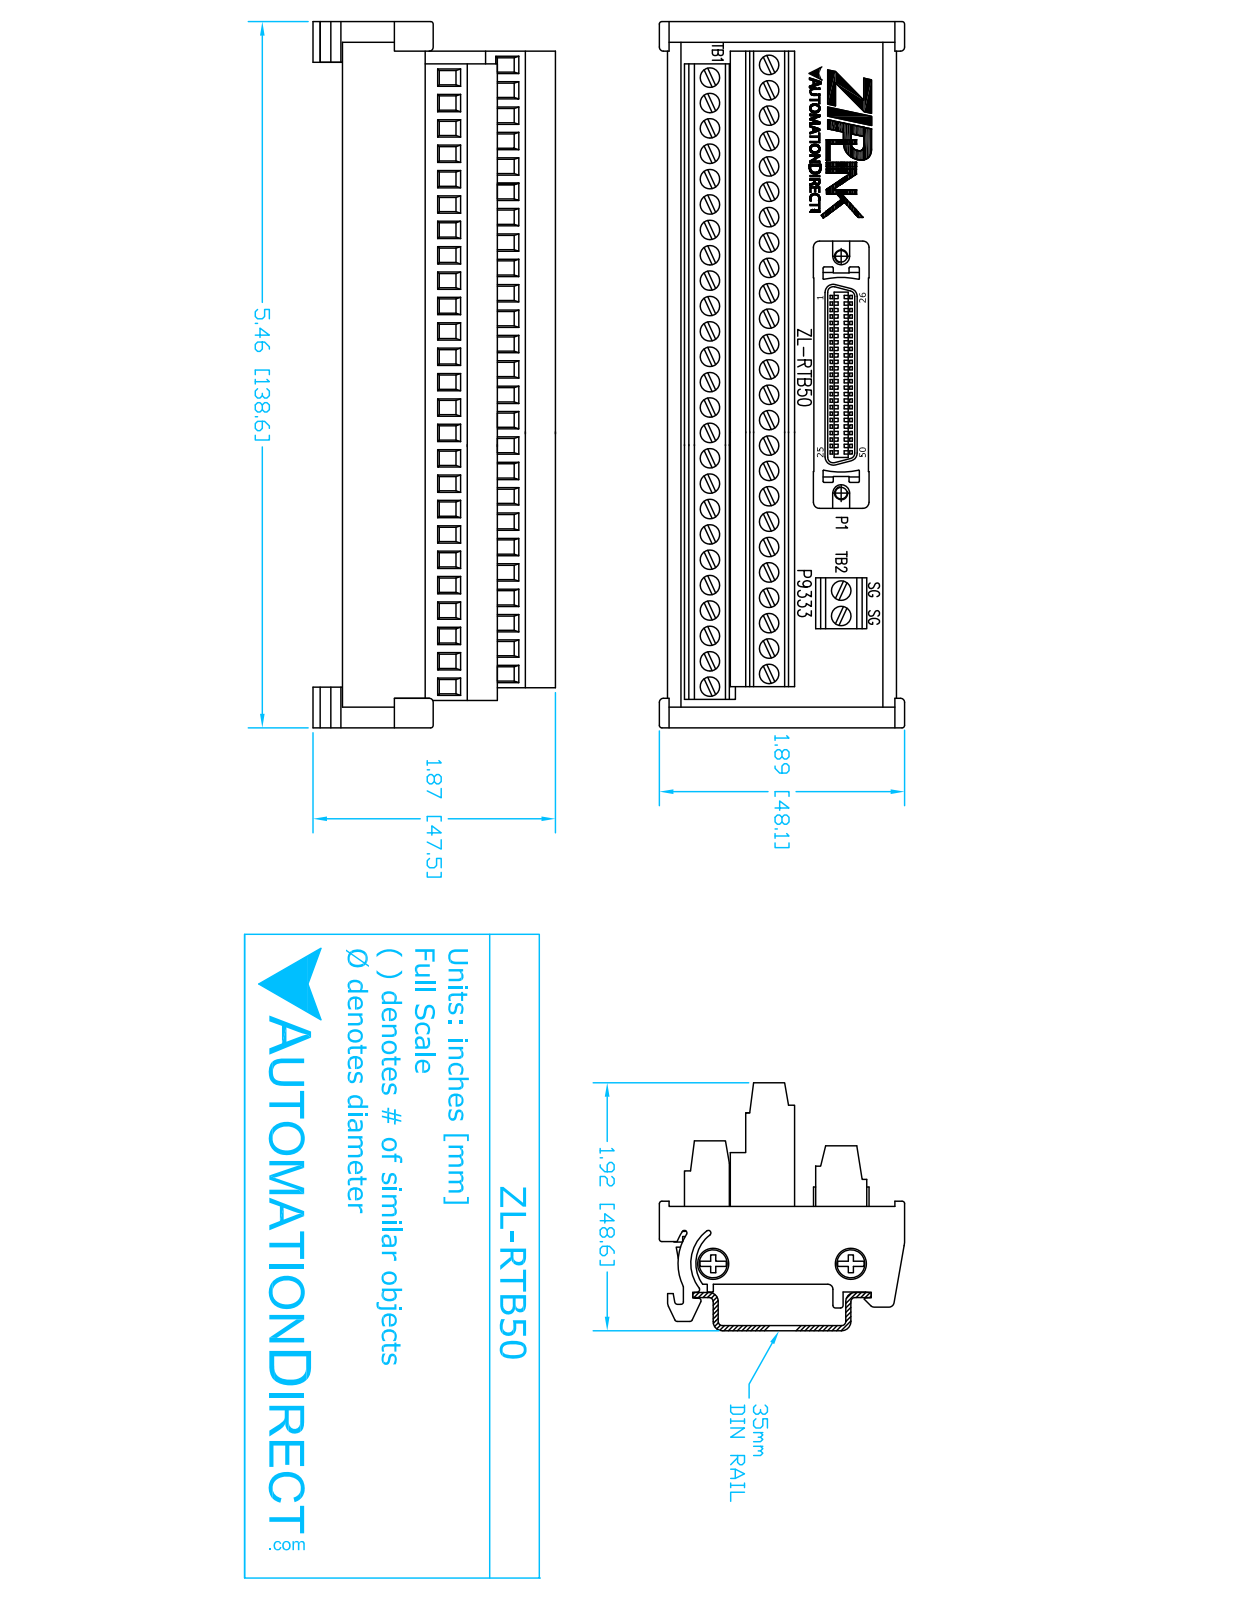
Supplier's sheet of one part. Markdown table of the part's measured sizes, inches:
| quantity | value |
| --- | --- |
| part name | ZL-RTB50 |
| STEP written by | SolidWorks 2014 (AUTOMOTIVE_DESIGN) |
| units | inches |
| bodies | 1 solid, 1307 faces (1145 planar, 158 cylindrical, 4 other) |
| overall size | 5.473 × 1.89 × 1.835 |
| volume | 8.728 in³ |
| surface area | 50.37 in² |
| round holes (diameter × count) | 0.148 × 50, 0.15 × 2, 0.235 × 2 |
| round bosses / shafts (diameter × count) | 0.2 × 2 |
| partial cylindrical surfaces (radius × count) | 0.015 × 12, 0.025 × 4, 0.04 × 4, 0.5 × 4, 0.233 × 1, 0.25 × 1, 0.327 × 1 |
| main face-to-face distances | 0.57, 0.03, 0.6, 0.455, 5.46, 1.79, 0.45, 1.12, 0.55, 0.52 |
| hole center spacings | 0.195, 0.585, 0.78, 1.365, 1.17, 1.95, 0.39, 1.755 |
